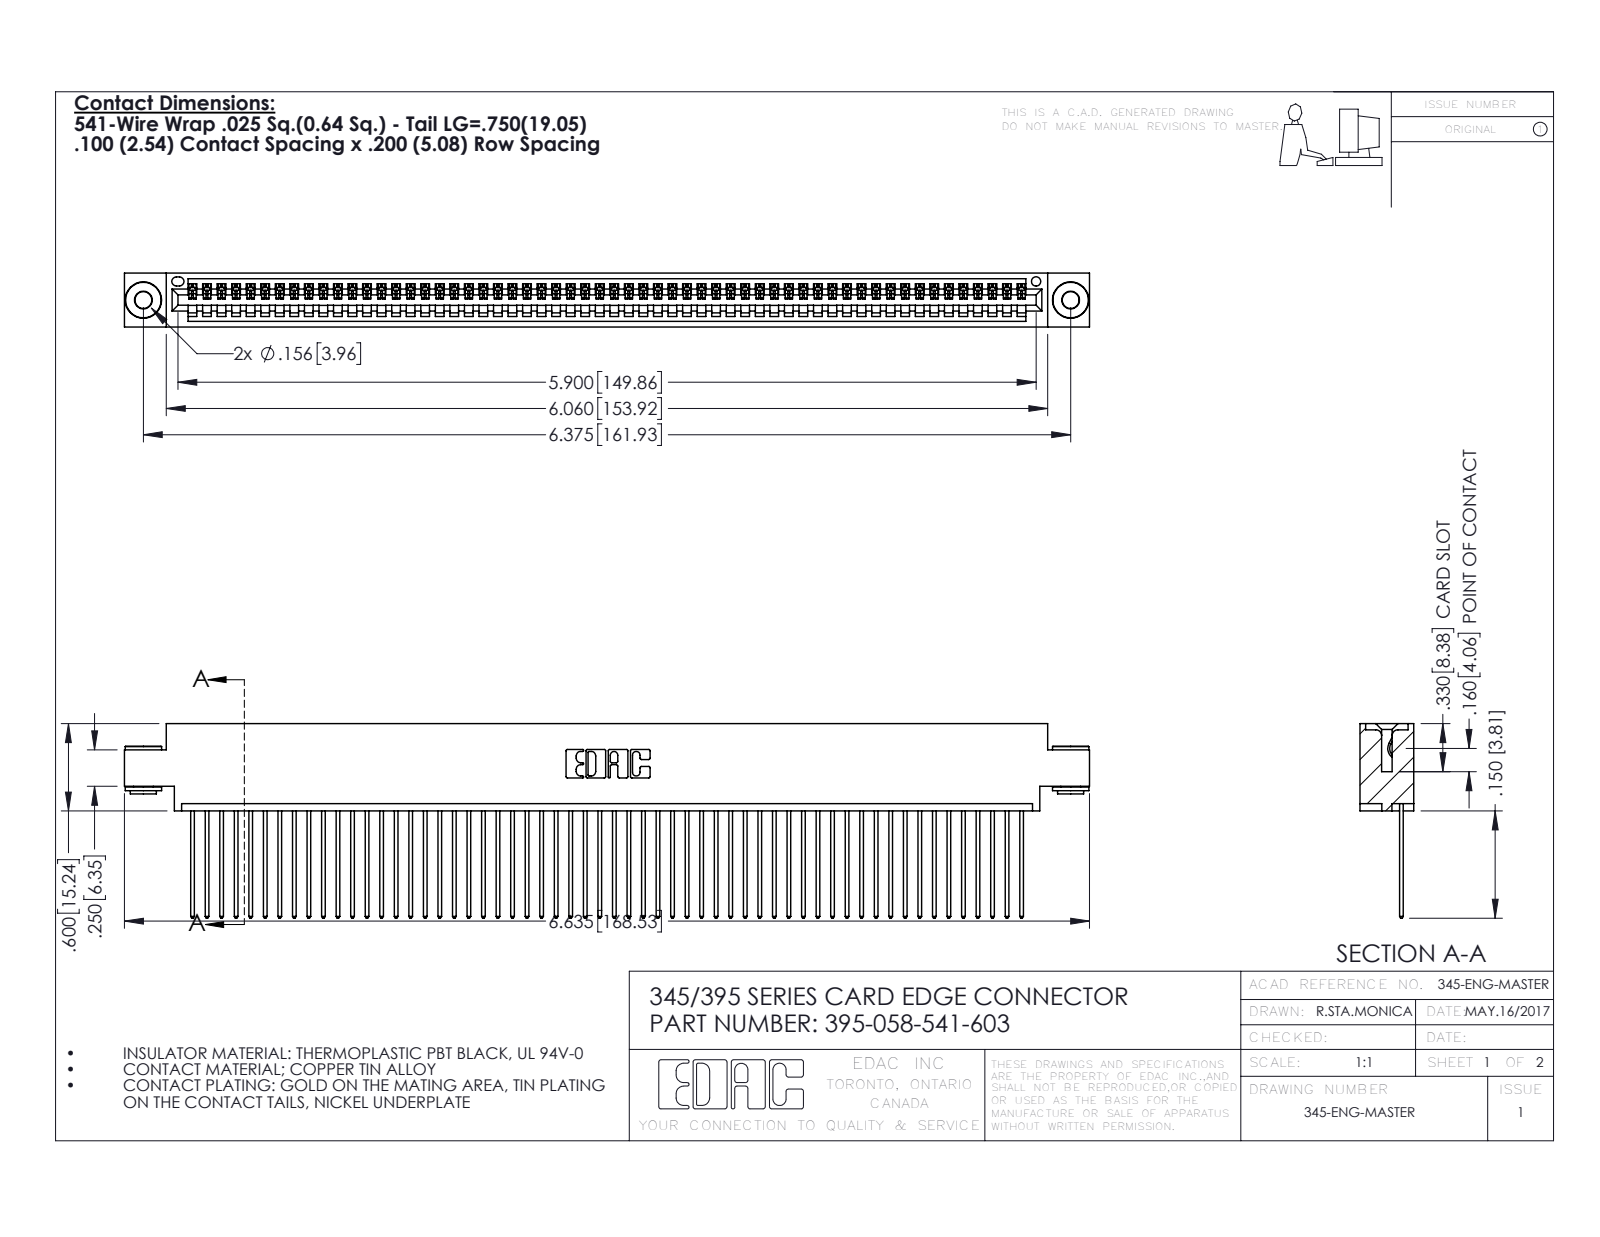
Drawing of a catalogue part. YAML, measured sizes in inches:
part_name: "395-058-541-603; 345-292-001_345-293-141; 345-250-002_345-250-002-102; 345 Part_0.170 Offset - 0.156 Dia-TH"
step_written_by: "SolidWorks 2016 (CONFIG_CONTROL_DESIGN)"
units: inches
bodies: {solids: 61, faces: 3532, planar: 2414, cylindrical: 1110, other: 8}
overall_size: [6.635, 1.337, 0.37]
volume: 0.991
surface_area: 36.05
round_holes:
  - {diameter: 0.116, count: 2}
  - {diameter: 0.156, count: 2}
  - {diameter: 0.064, count: 1}
round_bosses_or_shafts:
  - {diameter: 0.25, count: 2}
  - {diameter: 0.18, count: 2}
  - {diameter: 0.136, count: 2}
partial_cylinders:
  - {radius: 0.006, count: 116}
  - {radius: 0.01, count: 116}
  - {radius: 0.01, count: 22}
  - {radius: 0.007, count: 6}
  - {radius: 0.031, count: 6}
  - {radius: 0.026, count: 3}
  - {radius: 0.031, count: 2}
  - {radius: 0.04, count: 2}
face_to_face_distances: [0.072, 0.298, 0.37, 0.098, 0.272, 0.025, 0.2, 0.225, 0.175, 0.149]
hole_center_spacings: [0.27, 6.139, 6.375]
